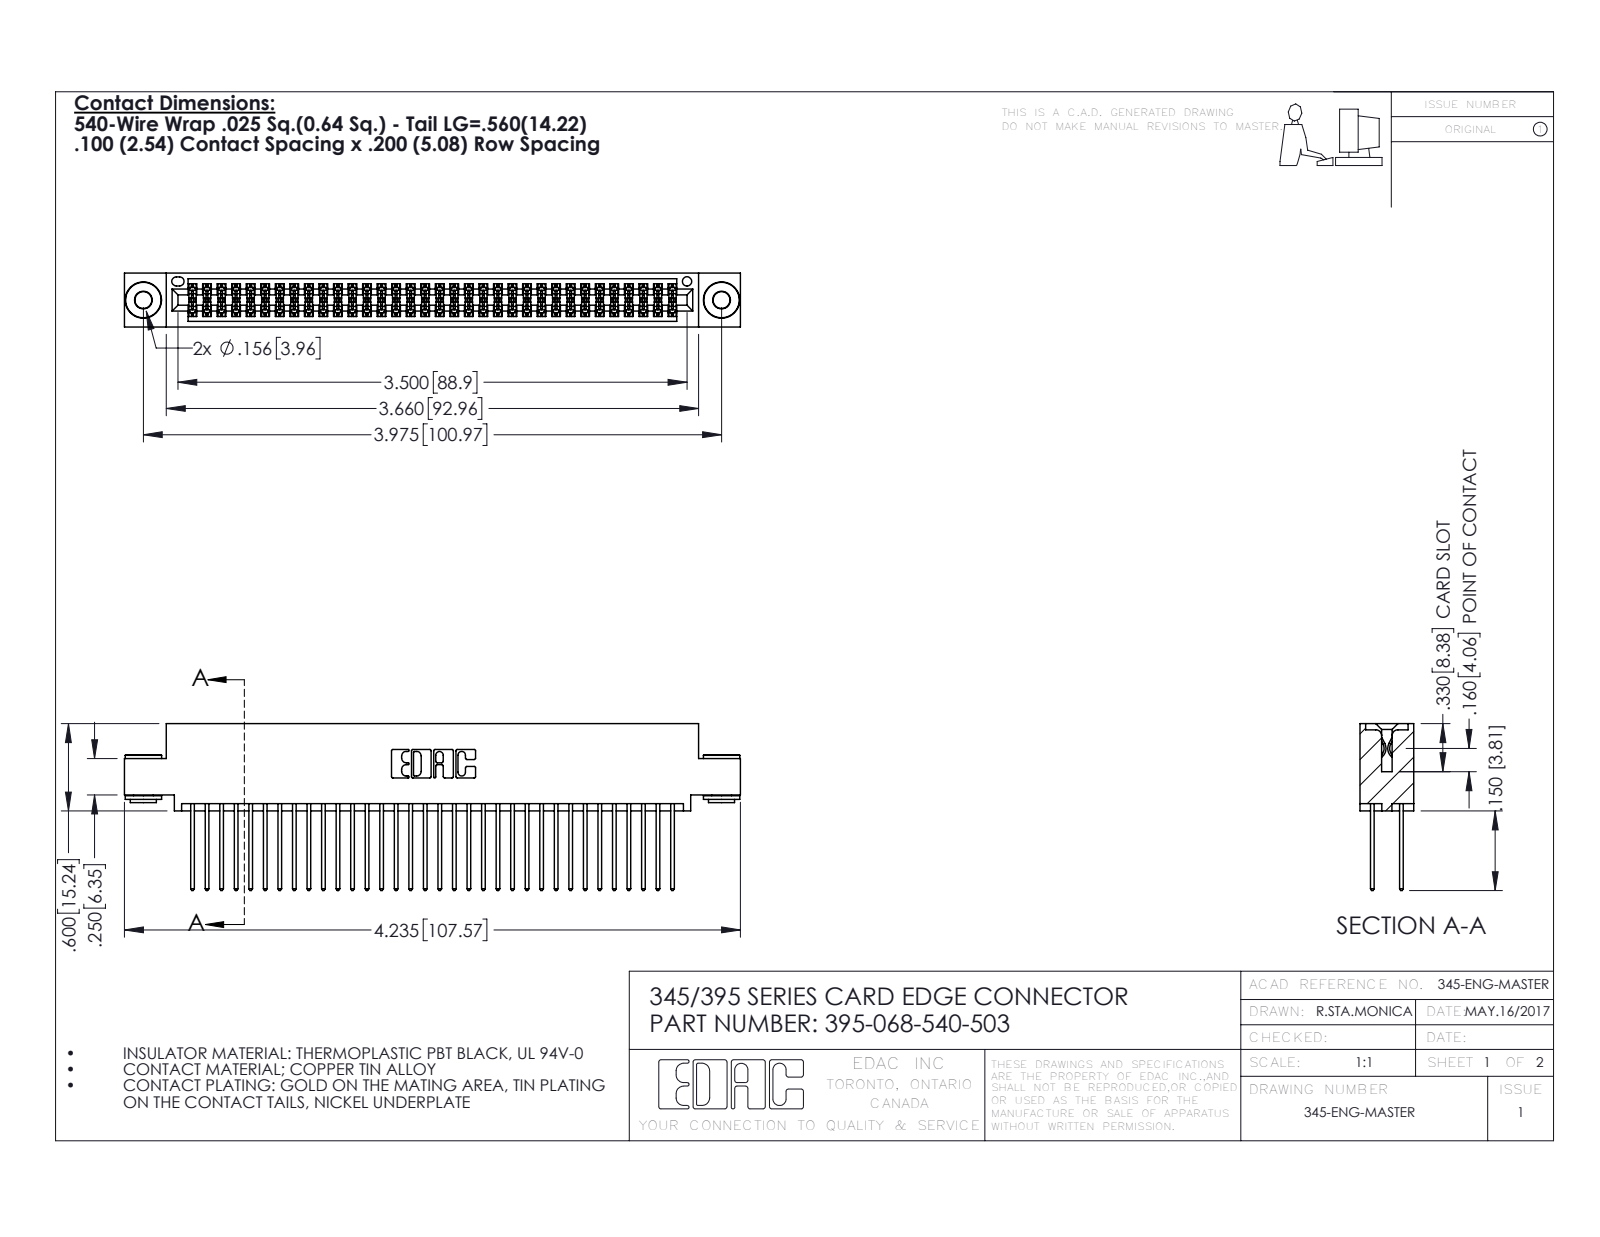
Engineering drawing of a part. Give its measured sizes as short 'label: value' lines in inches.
name: 395-068-540-503; 345-292-001_345-293-140; 345-250-002_345-250-002-102; 345 Part_0.110 Offset - 0.156 Dia-TH
written by: SolidWorks 2016 (CONFIG_CONTROL_DESIGN)
unit: in
bodies: 71 solids, 3568 faces (2338 planar, 1222 cylindrical, 8 other)
size: 4.235 × 1.147 × 0.37
volume: 0.646 in³; area: 26.31 in²
holes: 2× ⌀0.116, 2× ⌀0.156, 1× ⌀0.064
bosses: 2× ⌀0.25, 2× ⌀0.18, 2× ⌀0.136
rounds: 102× R0.006, 68× R0.01, 22× R0.01, 6× R0.007, 6× R0.031, 3× R0.026, 2× R0.014, 2× R0.019
face distances: 0.072, 0.298, 0.2, 0.025, 0.098, 0.272, 0.37, 0.225, 0.175, 0.149
hole spacings: 0.27, 3.74, 3.975
